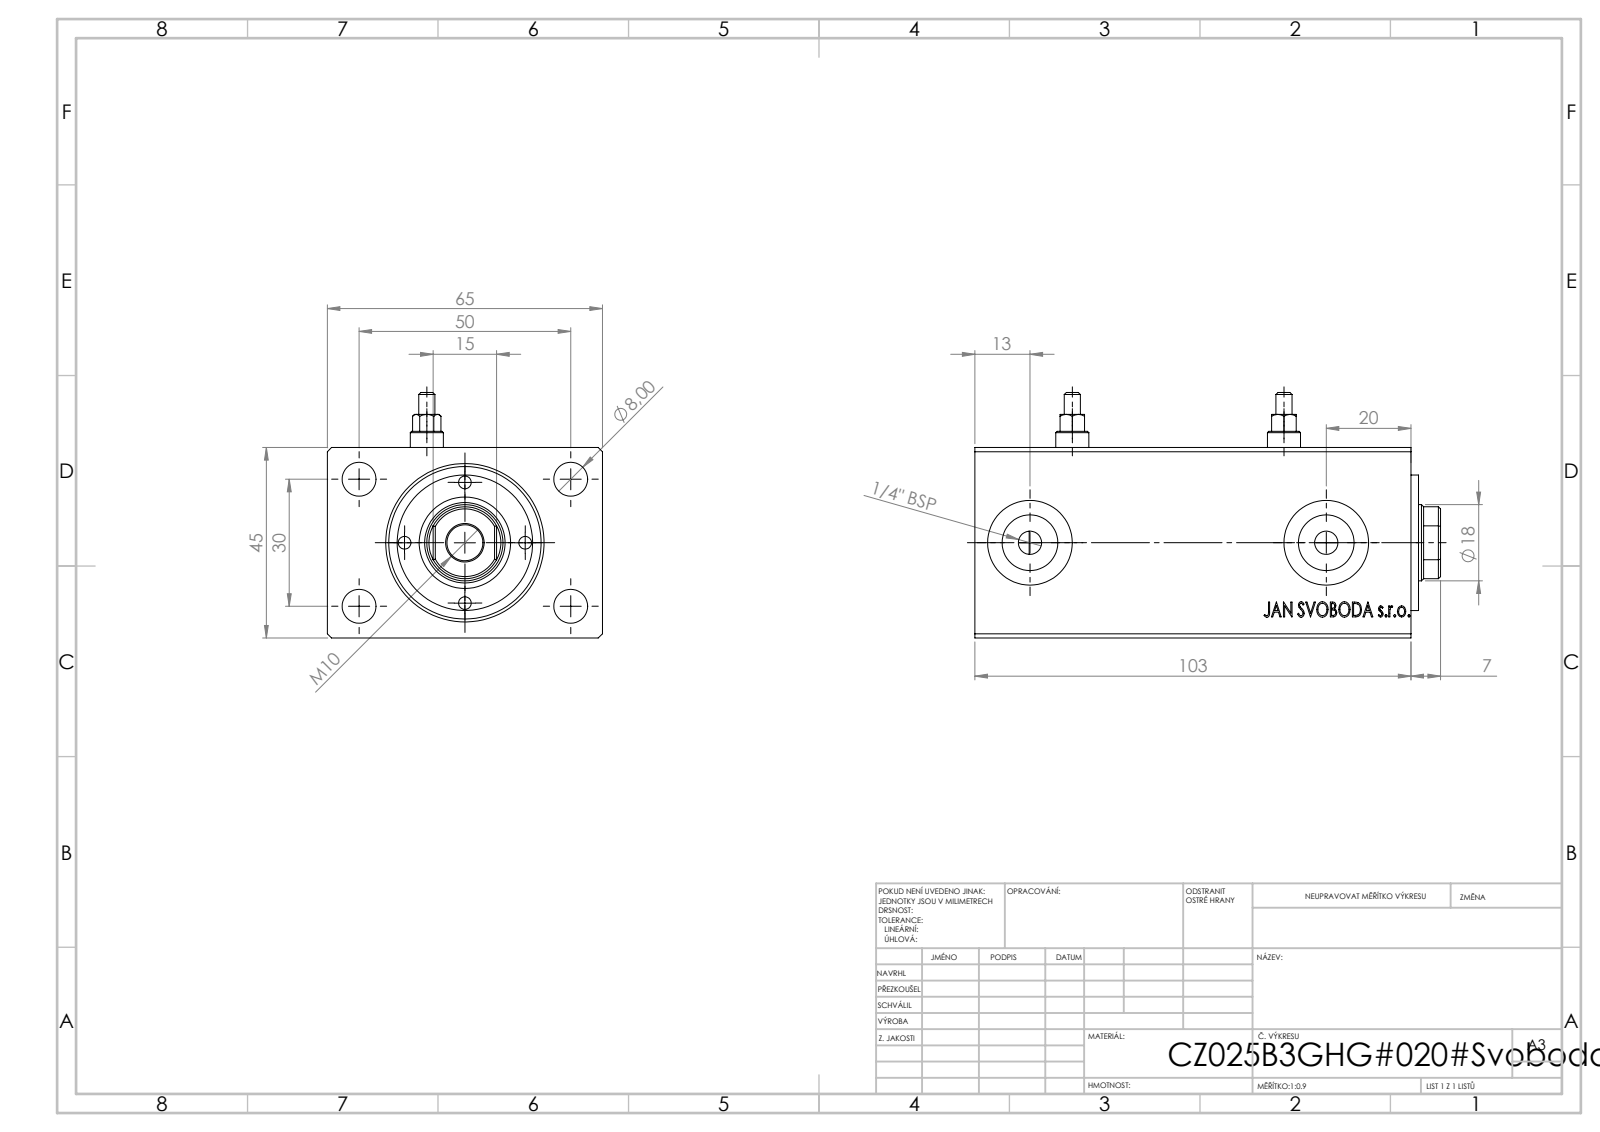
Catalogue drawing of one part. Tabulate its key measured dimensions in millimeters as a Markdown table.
| quantity | value |
| --- | --- |
| part name | Zatka_Cushioning3; V500CZ_B_VC; V500CZ |
| STEP written by | SolidWorks 2019 (CONFIG_CONTROL_DESIGN) |
| units | millimeters |
| bodies | 5 solids, 933 faces (423 planar, 74 cylindrical, 436 other) |
| overall size | 110 × 65 × 58 |
| volume | 282 743 mm³ |
| surface area | 53 676 mm² |
| round holes (diameter × count) | 8 × 6, 3 × 4, 1.8 × 2, 5.5 × 2, 13.16 × 2, 20 × 2, 8.5 × 1, 18 × 1, 19 × 1, 25 × 1, 36 × 1 |
| round bosses / shafts (diameter × count) | 7.8 × 2, 3.8 × 2, 32 × 1 |
| partial cylindrical surfaces (radius × count) | 8.5 × 1 |
| main face-to-face distances | 45, 65, 103, 7, 102.8, 12.8, 90.2, 12.6, 1.8, 5.2 |
| hole center spacings | 14.25, 18.45, 20.15, 25.01, 29.15, 38.48, 42.02, 50 |
